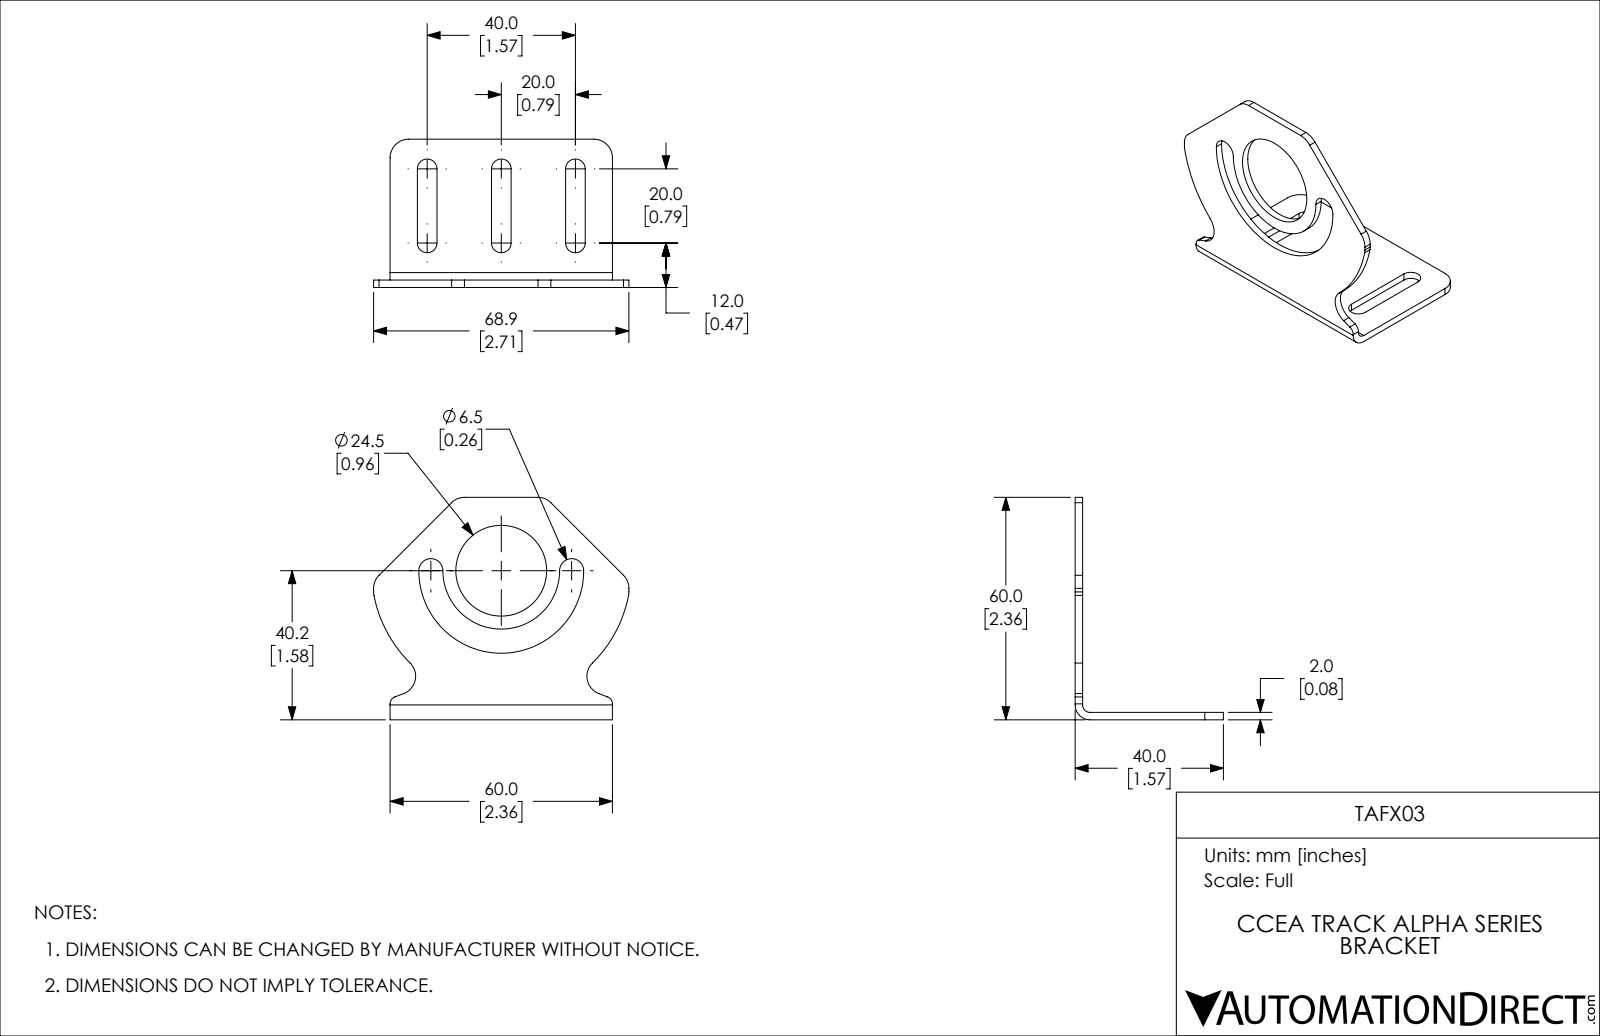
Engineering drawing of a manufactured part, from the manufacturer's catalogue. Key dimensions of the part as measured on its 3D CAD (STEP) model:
Part name (STEP PRODUCT): TAFX03
STEP written by: SolidWorks 2021 (CONFIG_CONTROL_DESIGN)
Units: inches
Bodies: 1 solid, 52 faces (20 planar, 32 cylindrical, 0 other)
Overall size (bounding box): 2.713 × 2.362 × 1.575
Volume: 0.508 in³ · Surface area: 15.04 in²
Round holes (diameter × count): ⌀0.965 ×1
Partial cylindrical surfaces — rounded edges, fillets, slot ends (radius × count): R0.197 ×8, R0.104 ×6, R0.079 ×3, R0.128 ×2, R0.193 ×2, R0.157 ×1, R0.62 ×1, R0.876 ×1
Main face-to-face distances: 0.079, 1.575, 0.787, 0.209, 2.362, 1.496, 0.289, 0.498, 1.077, 1.285
